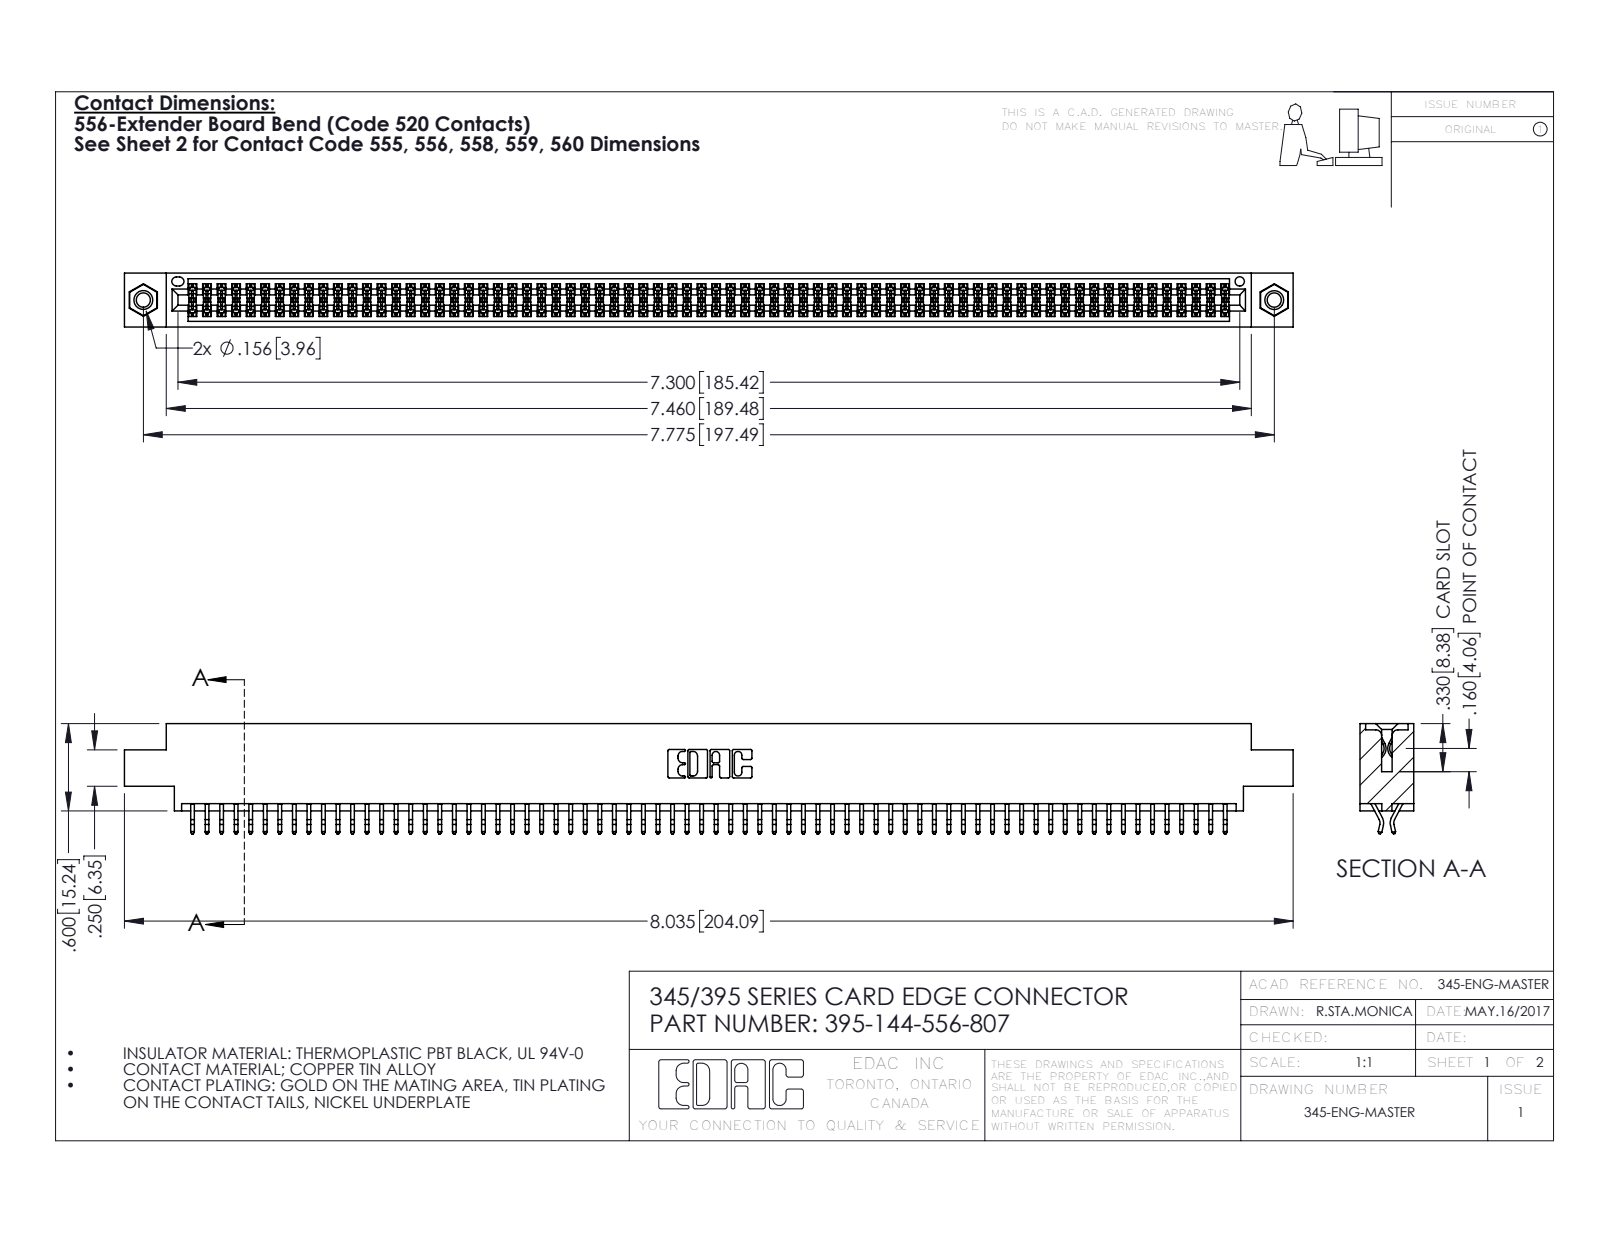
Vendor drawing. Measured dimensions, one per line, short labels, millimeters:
name: 345 Part_0.170 Offset - 0.156 Dia-TI; 345-292-001_556 Tail; 345-250-001_345-250-005-103; 395-144-556-807
written by: SolidWorks 2016 (CONFIG_CONTROL_DESIGN)
unit: mm
bodies: 147 solids, 8254 faces (5444 planar, 2794 cylindrical, 16 other)
size: 204.1 × 19.2 × 9.4
volume: 19 980 mm³; area: 30 150 mm²
holes: 2× ⌀2.5, 2× ⌀3.2, 2× ⌀4, 1× ⌀1.6
bosses: 2× ⌀3.9
rounds: 216× R0.2, 22× R0.3, 6× R0.2, 6× R0.8, 3× R0.7, 2× R0.3, 2× R0.4, 2× R0.5
face distances: 1.8, 7.6, 9.4, 5.1, 0.6, 2.5, 6.9, 5.7, 4.4, 3.8
hole spacings: 6.9, 191.5, 197.5
